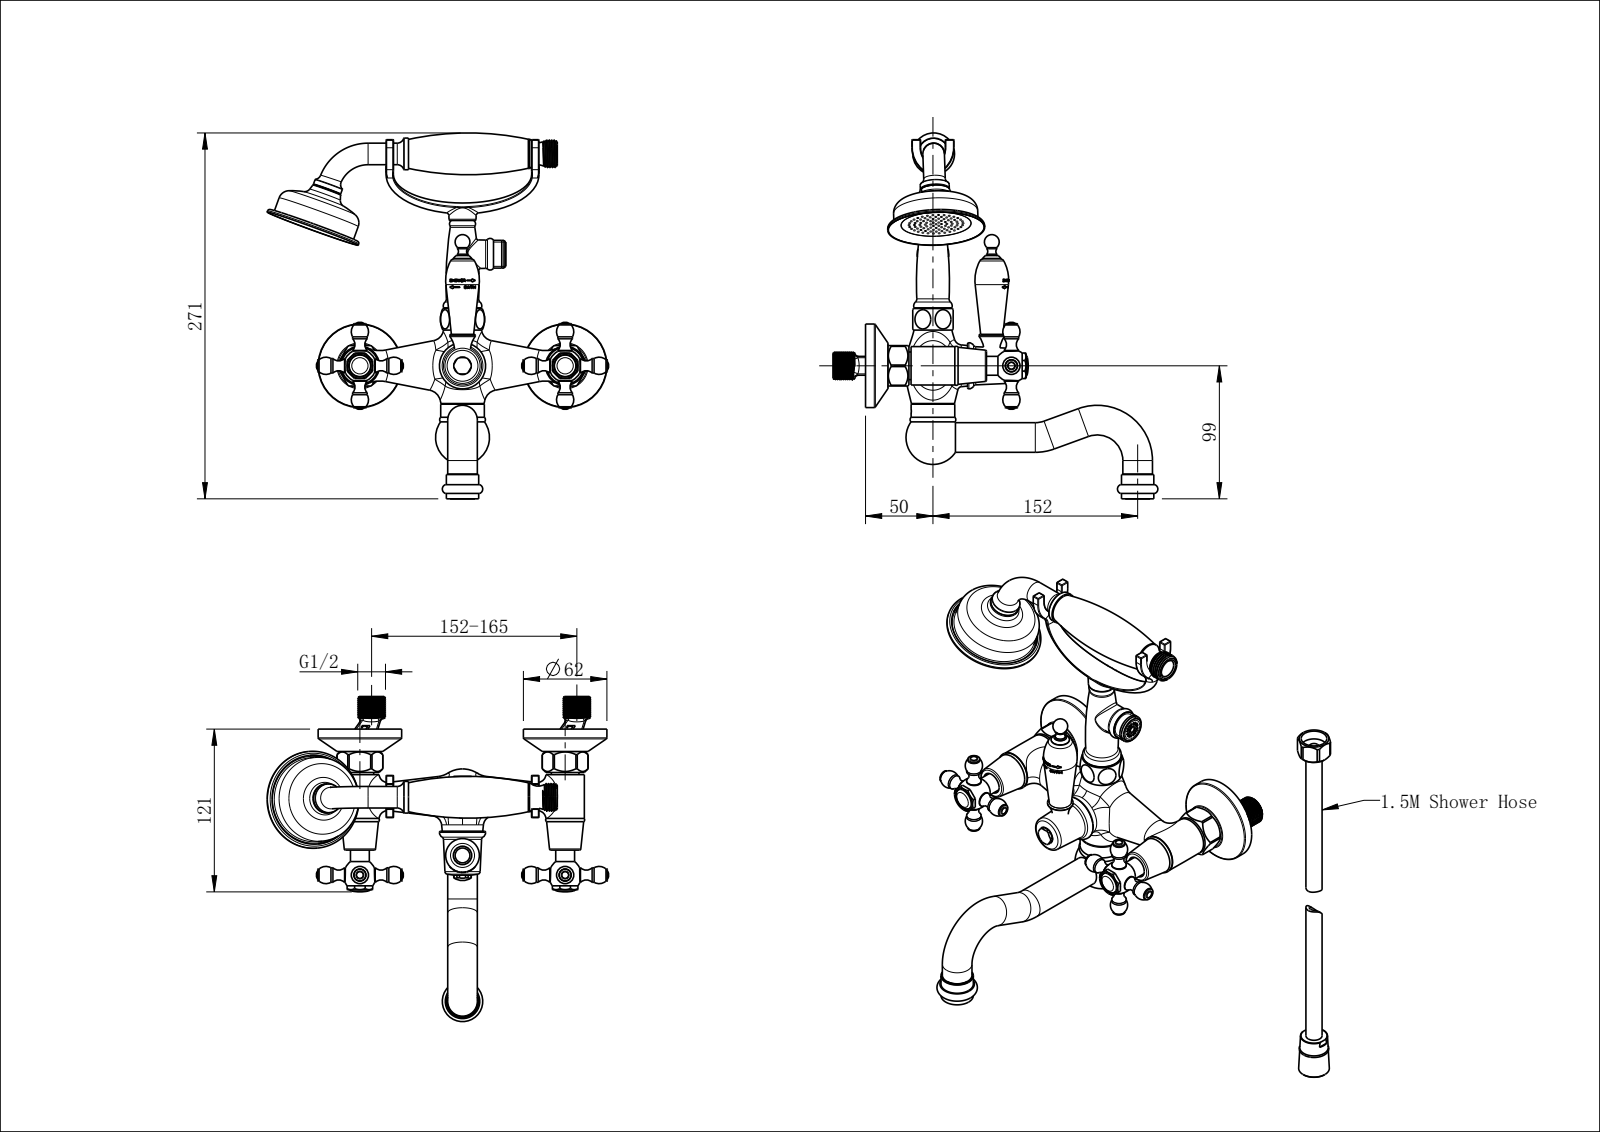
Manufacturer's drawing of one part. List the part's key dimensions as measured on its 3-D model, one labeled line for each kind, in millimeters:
Part name (STEP PRODUCT): MSBR-61; MSBR-60; MSBR-59; MSBR-58 (+8 more)
STEP written by: CREO PARAMETRIC BY PTC INC, 2015480 (AUTOMOTIVE_DESIGN)
Units: millimetres
Bodies: 62 solids, 5671 faces (2451 planar, 1405 cylindrical, 1815 other)
Overall size (bounding box): 502.32 × 302.75 × 241.72
Volume: 586 770 mm³ · Surface area: 292 364 mm²
Round holes (diameter × count): ⌀1 ×91, ⌀15 ×7, ⌀21 ×5, ⌀8 ×3, ⌀16.5 ×3, ⌀17 ×3, ⌀20 ×3, ⌀3.3 ×2, ⌀4.2 ×2, ⌀8.5 ×2, ⌀9.5 ×2, ⌀10 ×2
Round bosses / shafts (diameter × count): ⌀22 ×6, ⌀16 ×6, ⌀24 ×5, ⌀20.6 ×5, ⌀23.5 ×4, ⌀18 ×4, ⌀18.5 ×3, ⌀14 ×3
Partial cylindrical surfaces — rounded edges, fillets, slot ends (radius × count): R0.2 ×40, R0.5 ×24, R1 ×18, R1.5 ×6, R0.8 ×4, R1.7 ×4, R4 ×4, R6.5 ×3
Main face-to-face distances: 2, 2.5, 32.5, 9.75, 19.75, 29.5, 34.2, 91, 131.98, 41
Hole centre spacings: 8.02, 12.03, 10.61, 4.01, 4.97, 6.95, 14.46, 4.15
